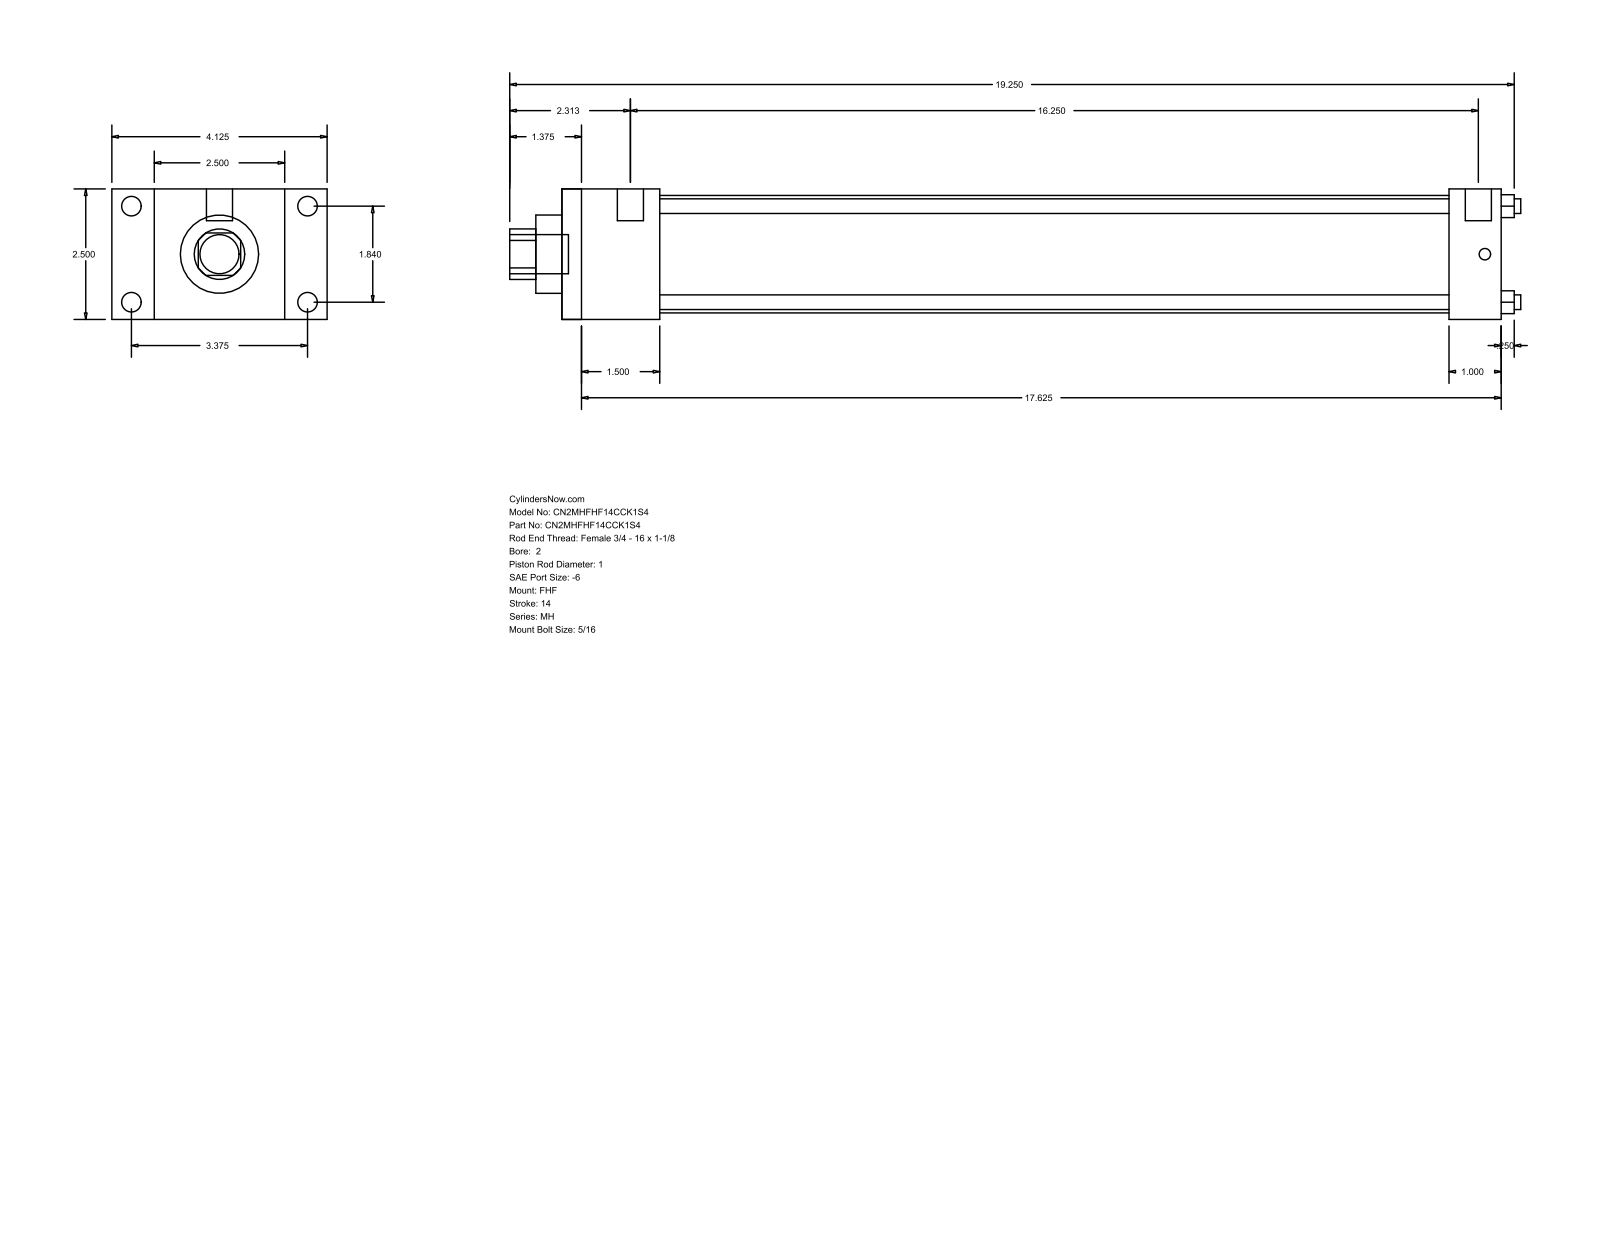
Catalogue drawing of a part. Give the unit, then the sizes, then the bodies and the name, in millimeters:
Units: millimetres
Overall size (bounding box): 492.12 × 104.78 × 63.5
Round holes (diameter × count): ⌀7.14 ×4, ⌀25.4 ×1, ⌀38.1 ×1, ⌀57.15 ×1
Round bosses / shafts (diameter × count): ⌀9.53 ×4, ⌀5.56 ×4, ⌀12.7 ×2, ⌀19.05 ×1
Partial cylindrical surfaces — rounded edges, fillets, slot ends (radius × count): R12.29 ×1
Main face-to-face distances: 63.5, 457.2, 47.63, 409.57, 20.64, 84.14, 104.78, 25.4, 431.8, 384.17
Hole centre spacings: 33.05, 46.74, 66.1
Bodies: 0 solids, 88 faces (60 planar, 28 cylindrical, 0 other)
Part name (STEP PRODUCT): MH_FHF__0200_1
STEP written by: GSSL Pune (CONFIG_CONTROL_DESIGN)
